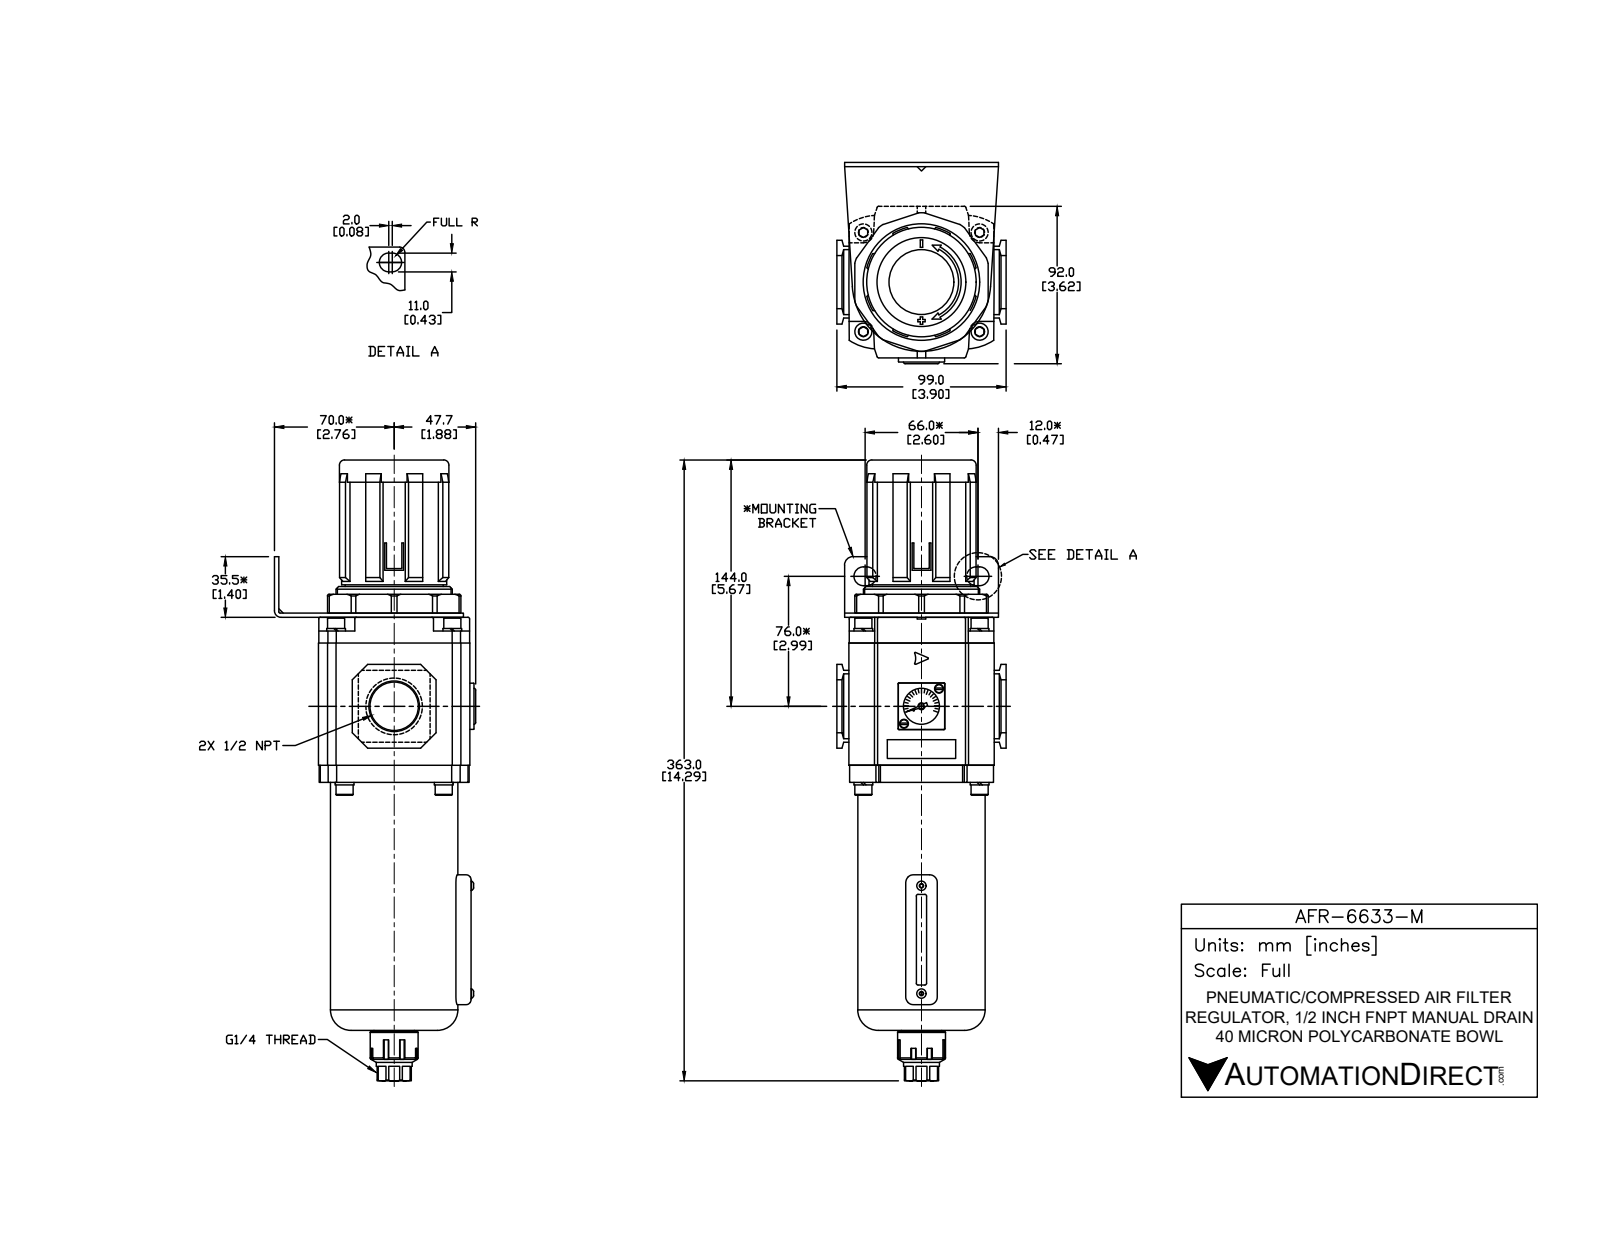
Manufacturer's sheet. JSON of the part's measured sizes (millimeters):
{"part_name": "AFR-6633-M", "step_written_by": "SolidWorks 2015 (CONFIG_CONTROL_DESIGN)", "units": "millimeters", "bodies": {"solids": 16, "faces": 703, "planar": 439, "cylindrical": 175, "other": 89}, "overall_size": [362.7, 117, 99], "volume_mm3": 1686000, "surface_area_mm2": 184625, "round_holes": [[3, 6], [2, 1], [12, 1], [23.01, 1], [30, 1], [38, 1]], "round_bosses_or_shafts": [[10, 8], [5.5, 2], [2.7, 2], [68, 1], [64, 1], [62, 1], [53.76, 1], [28, 1]], "partial_cylinders_radius": [[1, 12], [1.2, 10], [1.3, 8], [2.5, 8], [9.5, 8], [19.9, 8], [0.5, 6], [0.3, 4]], "face_to_face_distances": [2.5, 91.2, 88.7, 87.6, 1, 88.6, 92, 85, 10, 7], "hole_center_spacings": [41.35, 34.68, 53.16, 63.36, 82.71, 69.35]}
